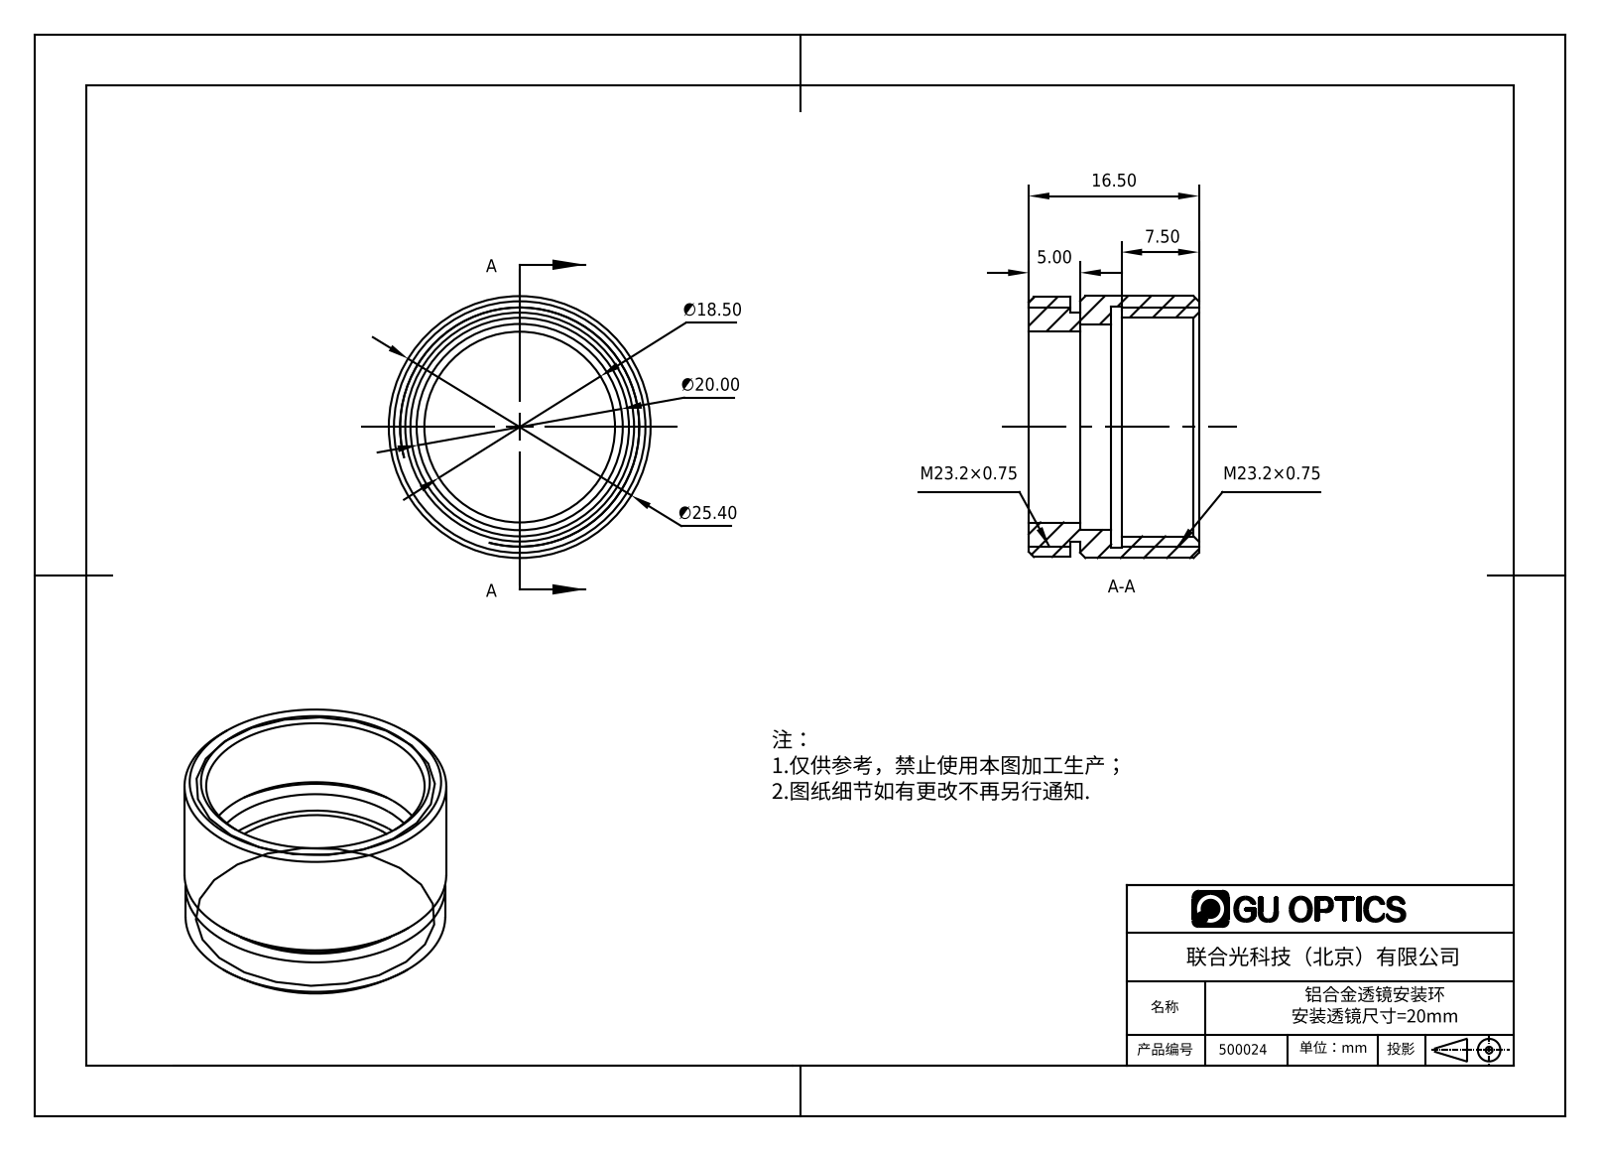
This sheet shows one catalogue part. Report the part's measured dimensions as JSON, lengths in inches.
{"part_name": "500024", "step_written_by": "SolidWorks 2016 (AUTOMOTIVE_DESIGN)", "units": "inches", "bodies": {"solids": 1, "faces": 29, "planar": 7, "cylindrical": 14, "other": 8}, "overall_size": [1, 1, 0.65], "volume_in3": 0.169, "surface_area_in2": 4.841, "round_holes": [[0.728, 1], [0.787, 1], [0.835, 1], [0.921, 1]], "round_bosses_or_shafts": [[1, 1], [0.992, 1], [0.874, 1]], "face_to_face_distances": [0.157, 0.039, 0.118, 0.197, 0.276, 0.079, 0.65, 0.492, 0.453, 0.374]}
